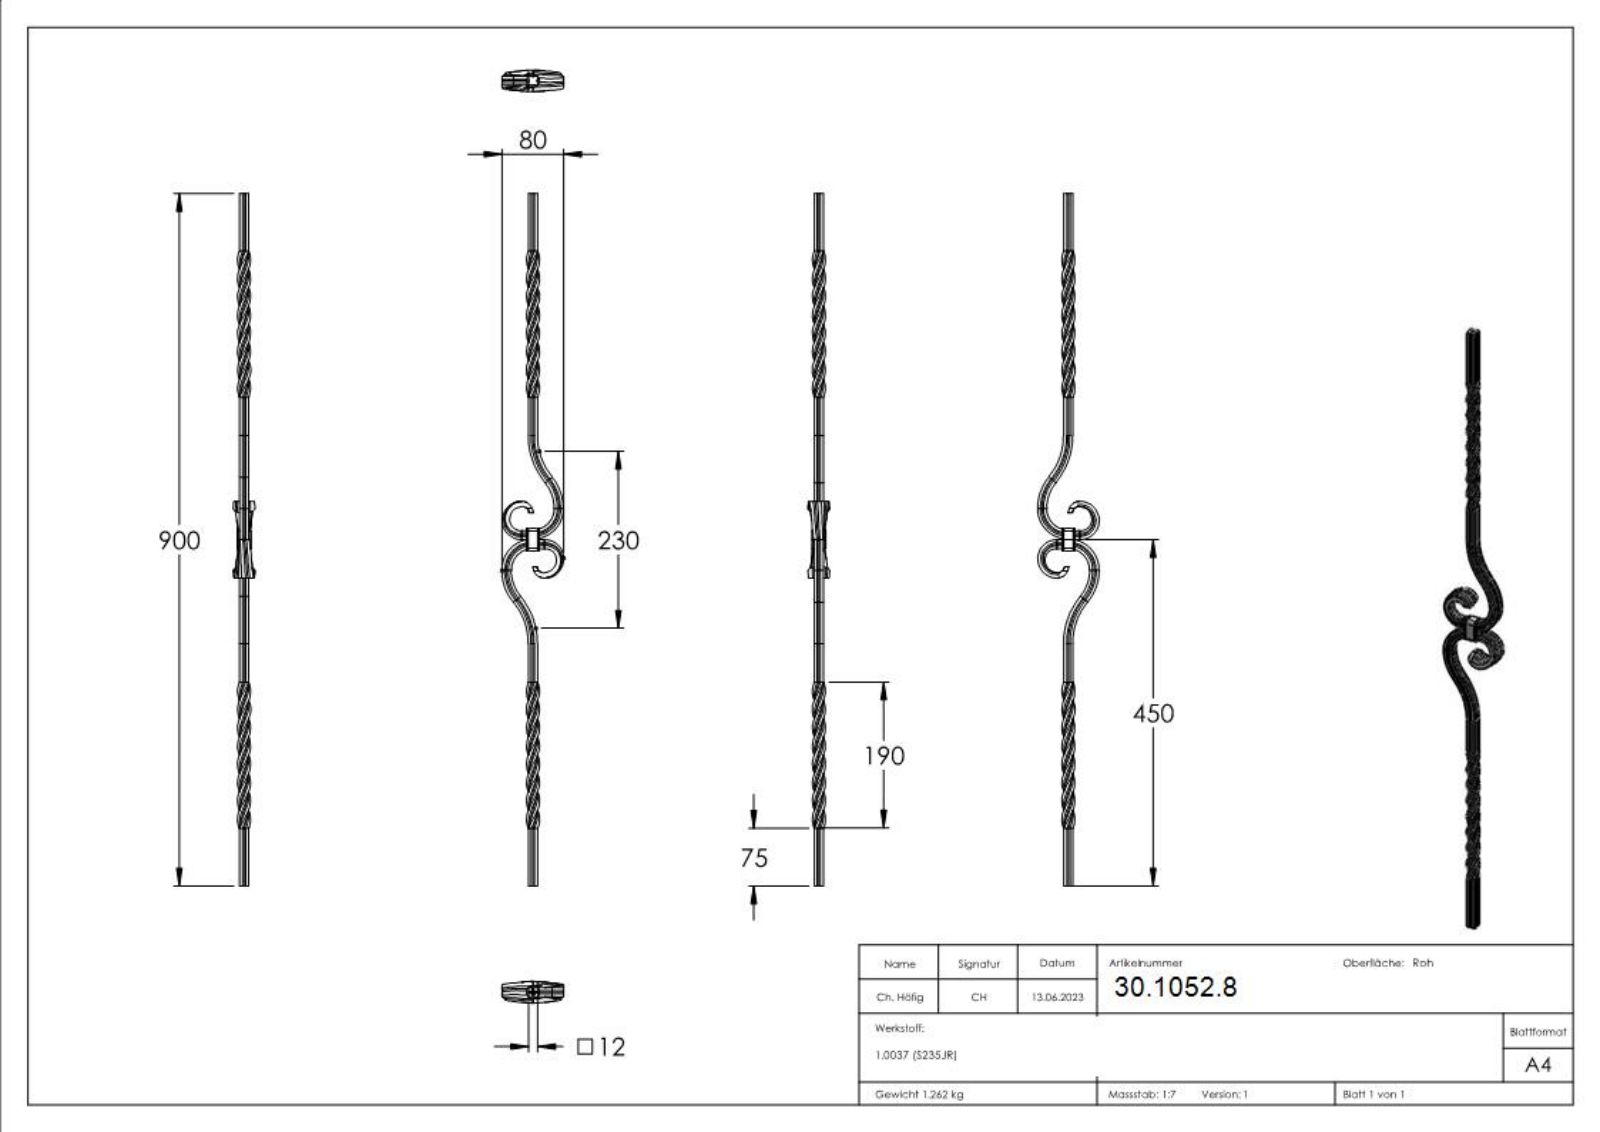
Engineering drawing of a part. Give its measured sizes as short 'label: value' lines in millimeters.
name: 1208
written by: SolidWorks 2018 (CONFIG_CONTROL_DESIGN)
unit: mm
bodies: 6 solids, 631 faces (280 planar, 81 cylindrical, 270 other)
size: 900 × 80 × 28.26
volume: 174 813 mm³; area: 67 486 mm²
rounds: 24× R0.5, 8× R0.2, 4× R1, 4× R4, 4× R20.14, 2× R28, 2× R40, 2× R53
face distances: 12, 8.94, 9, 21, 23, 7, 14, 2, 30, 24
